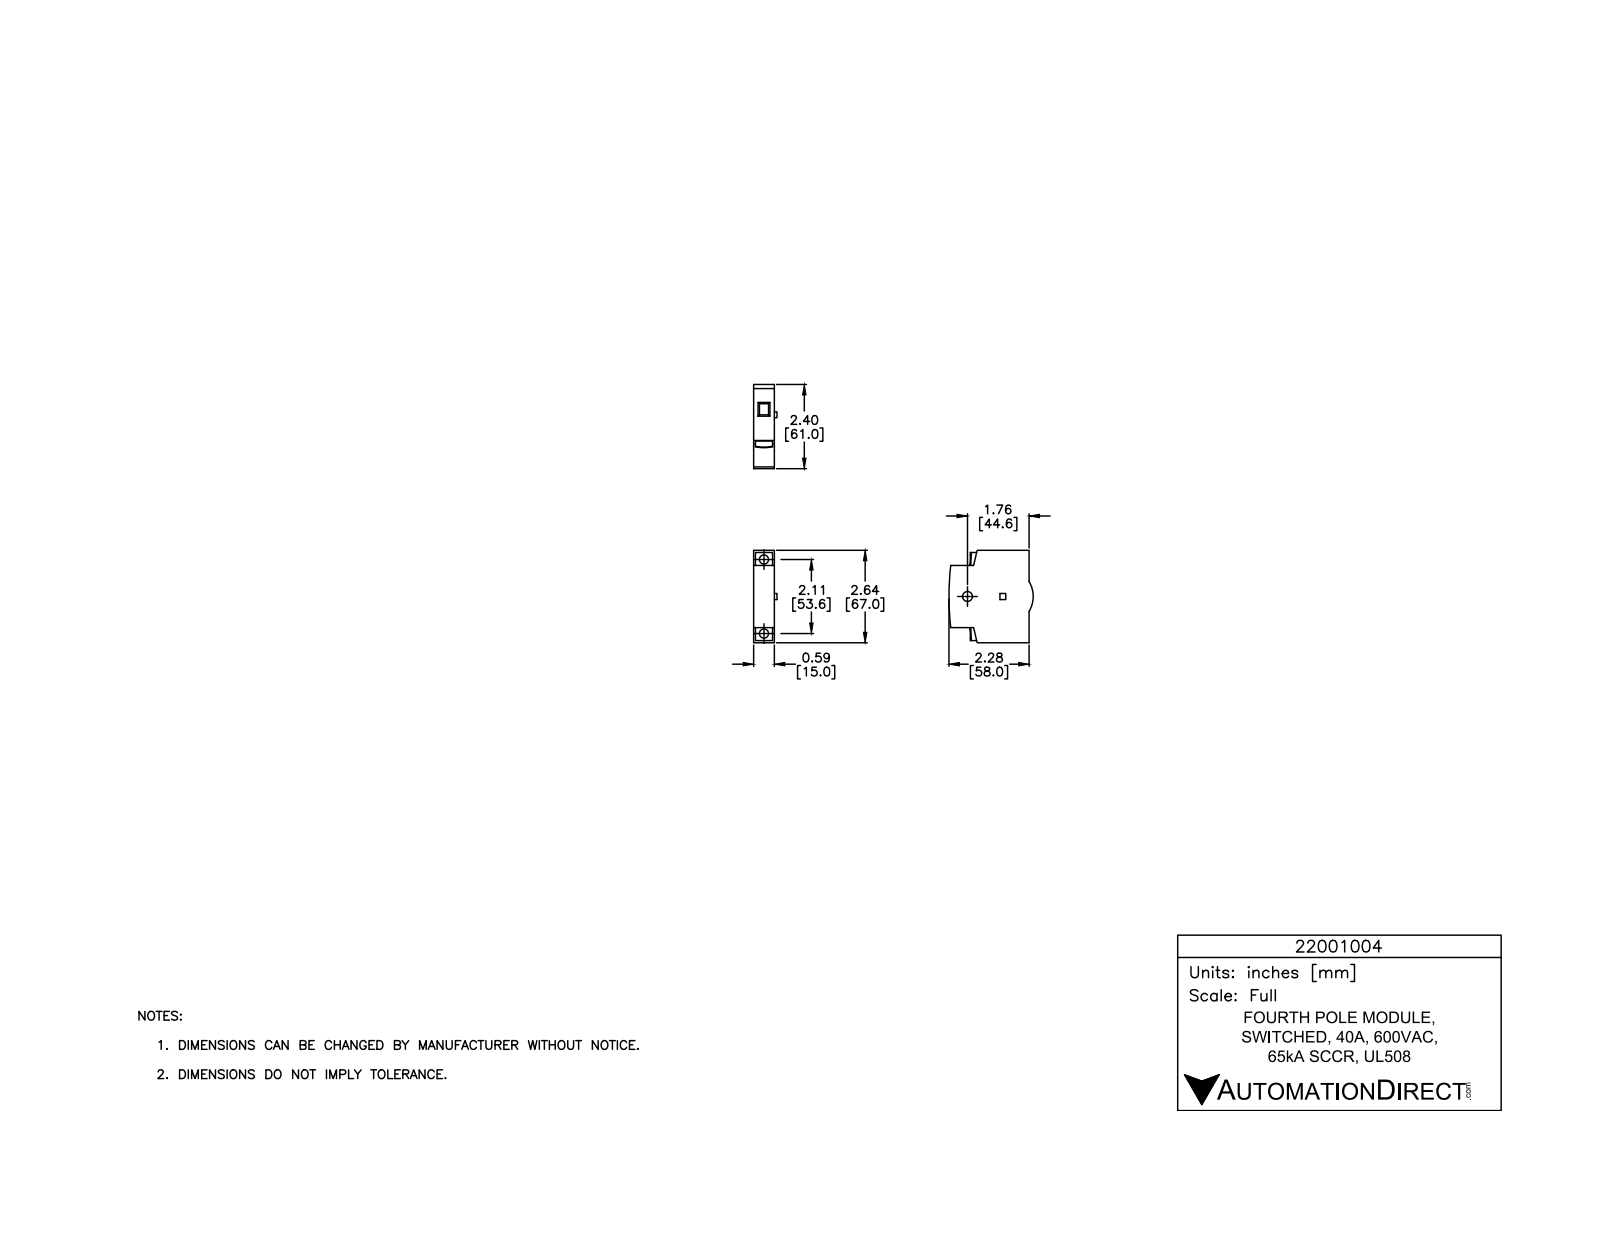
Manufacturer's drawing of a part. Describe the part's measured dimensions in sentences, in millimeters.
The part is named "22001004-UL". Its 3-D file was written by "SolidWorks 2021 (CONFIG_CONTROL_DESIGN)". It is 1 solid with 61 faces: 46 planar, 11 cylindrical and 4 other. Overall it measures 67 by 61 by 16.9 millimeters. Its volume is 51 470 cubic millimeters and its surface area 11 700 square millimeters. Round holes: 2 of diameter 6.6, 1 of diameter 7.2. Partial cylindrical surfaces (rounded edges, fillets, slot ends): 1 of radius 21, 1 of radius 200. The main face-to-face distances are 15, 67, 11, 56, 45, 1.6, 65.4, 9.4, 54.4, 1.3. The hole center spacings are 53.6.
